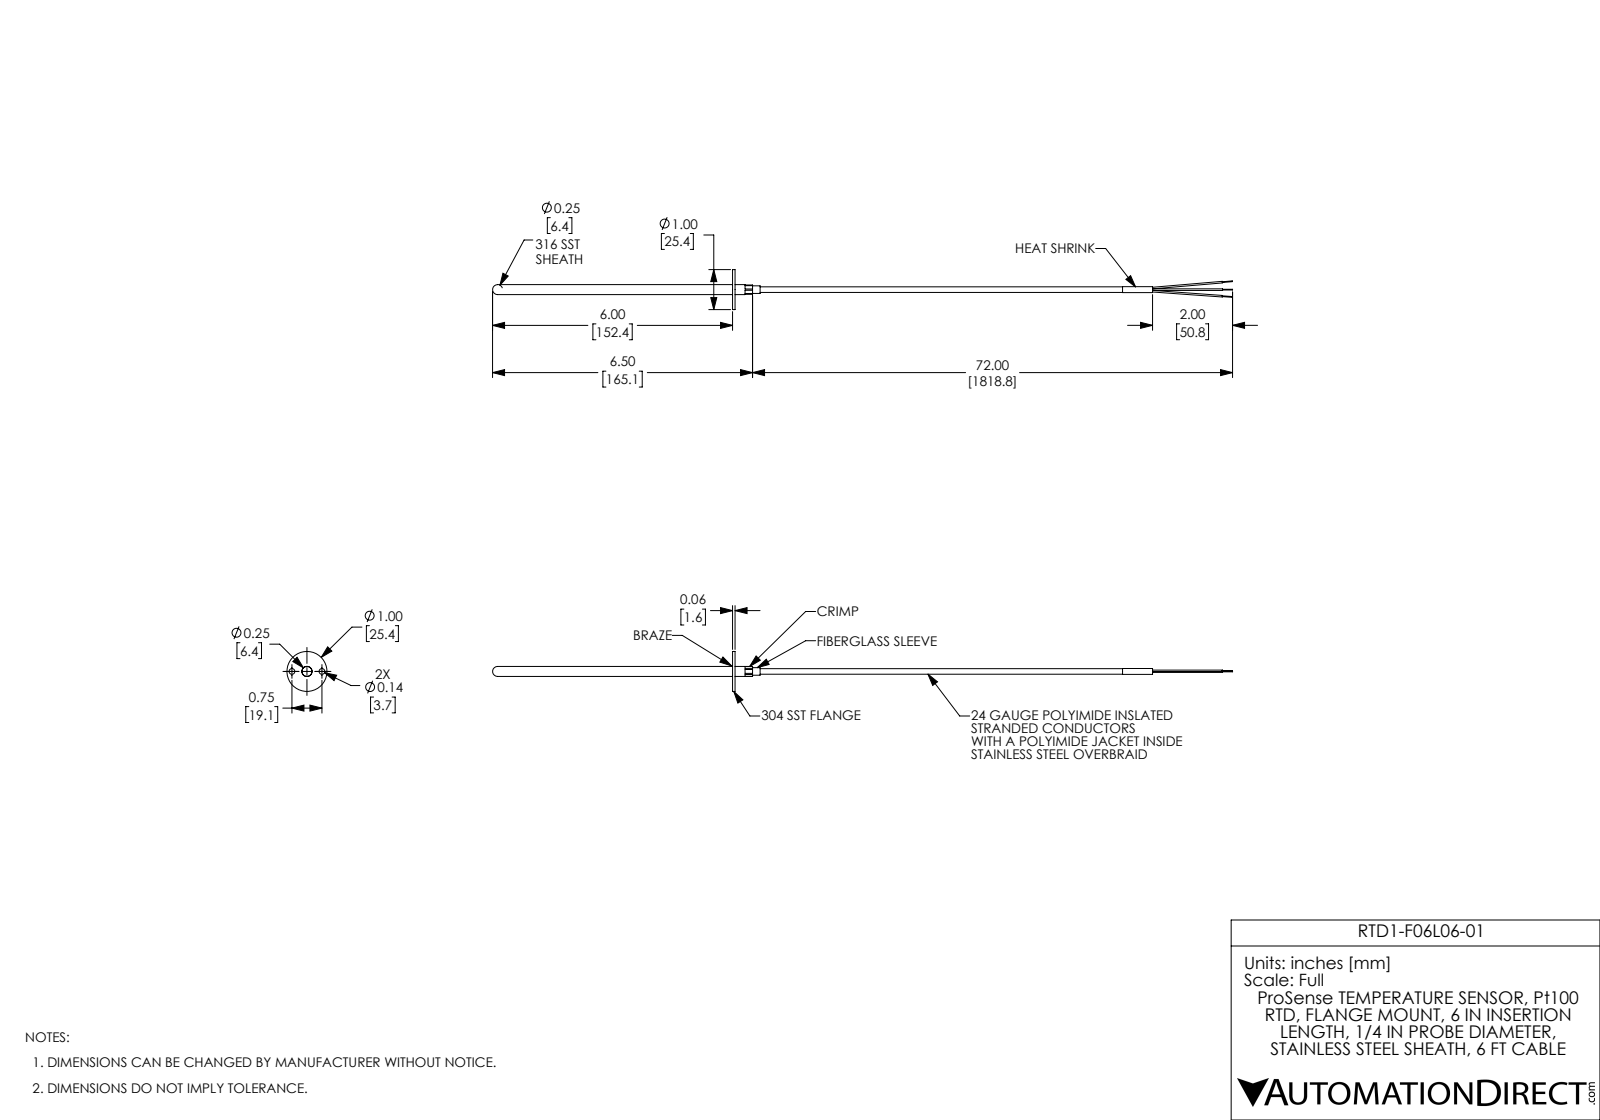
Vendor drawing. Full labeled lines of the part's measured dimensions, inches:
Part name (STEP PRODUCT): RTD1-F06L06-01
STEP written by: SolidWorks 2017 (AUTOMOTIVE_DESIGN)
Units: inches
Bodies: 7 solids, 70 faces (31 planar, 32 cylindrical, 7 other)
Overall size (bounding box): 18.5 × 1 × 1
Volume: 0.534 in³ · Surface area: 22.49 in²
Round holes (diameter × count): ⌀0.144 ×3, ⌀0.136 ×1, ⌀0.189 ×1, ⌀0.257 ×1
Round bosses / shafts (diameter × count): ⌀1 ×1, ⌀0.25 ×1, ⌀0.19 ×1, ⌀0.188 ×1, ⌀0.148 ×1, ⌀0.14 ×1, ⌀0.132 ×1, ⌀0.04 ×1
Main face-to-face distances: 0.063, 0.5, 0.437, 0.231, 0.188, 0.75, 0.062, 0.124, 0.562, 0.688
Hole centre spacings: 0.375, 0.375, 0.75
